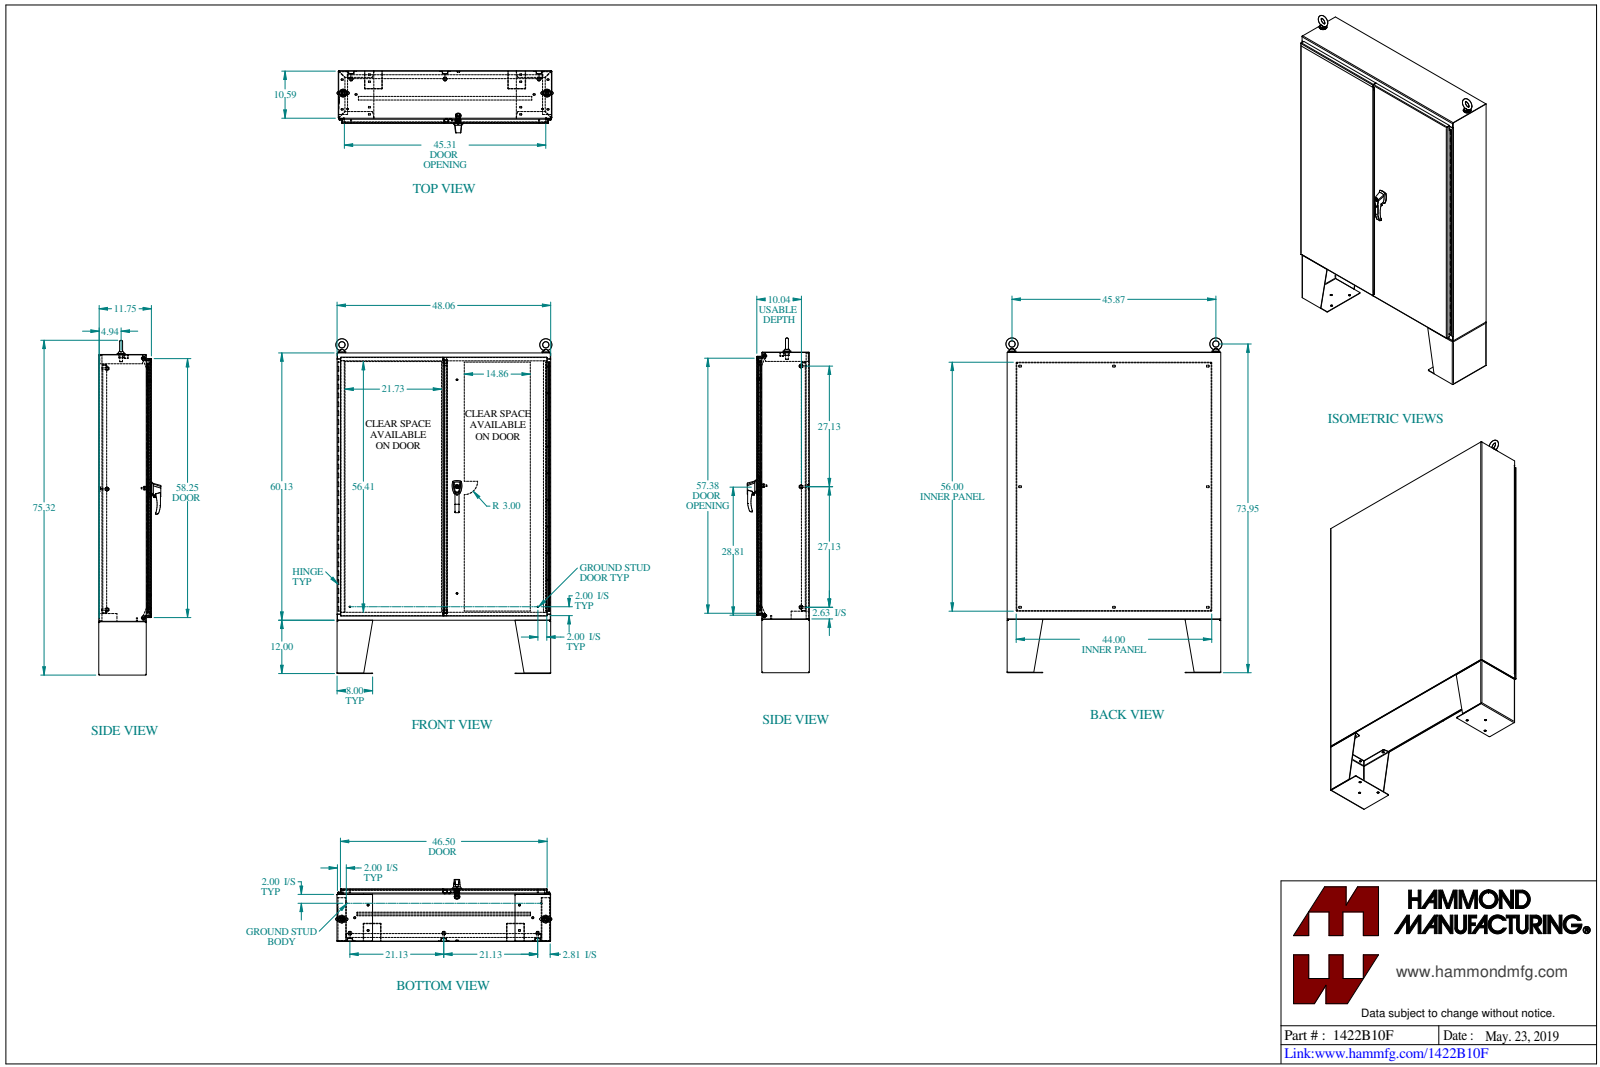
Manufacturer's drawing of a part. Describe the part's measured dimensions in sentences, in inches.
The part is named "1422B10F_Default". Its 3-D file was written by "SolidWorks 2019 (CONFIG_CONTROL_DESIGN)". It is 90 solids with 2769 faces: 1280 planar, 1242 cylindrical and 247 other. Overall it measures 75.778 by 49.121 by 13.963 inches. Its volume is 1 376 cubic inches and its surface area 27 327 square inches. Round holes: 20 of diameter 0.304, 14 of diameter 0.437, 9 of diameter 0.307, 8 of diameter 0.563, 6 of diameter 0.445, 2 of diameter 0.11, 2 of diameter 0.25, 2 of diameter 0.257, 2 of diameter 0.28, 2 of diameter 0.281, 2 of diameter 0.313, 2 of diameter 0.39. Round bosses or shafts: 10 of diameter 1, 8 of diameter 0.65, 8 of diameter 0.375, 8 of diameter 0.33, 6 of diameter 0.281, 4 of diameter 0.25, 2 of diameter 1.75, 2 of diameter 1.5. Partial cylindrical surfaces (rounded edges, fillets, slot ends): 32 of radius 0.048, 32 of radius 0.143, 22 of radius 0.125, 16 of radius 0.018, 14 of radius 0.06, 12 of radius 0.116, 8 of radius 0.05, 8 of radius 0.185. The main face-to-face distances are 0.095, 0.095, 11.658, 11.753, 11.753, 11.848, 0.125, 10.066, 9.971, 1.687. The hole center spacings are 6, 46.778, 12, 47.919, 18, 49.762, 24, 52.232.
